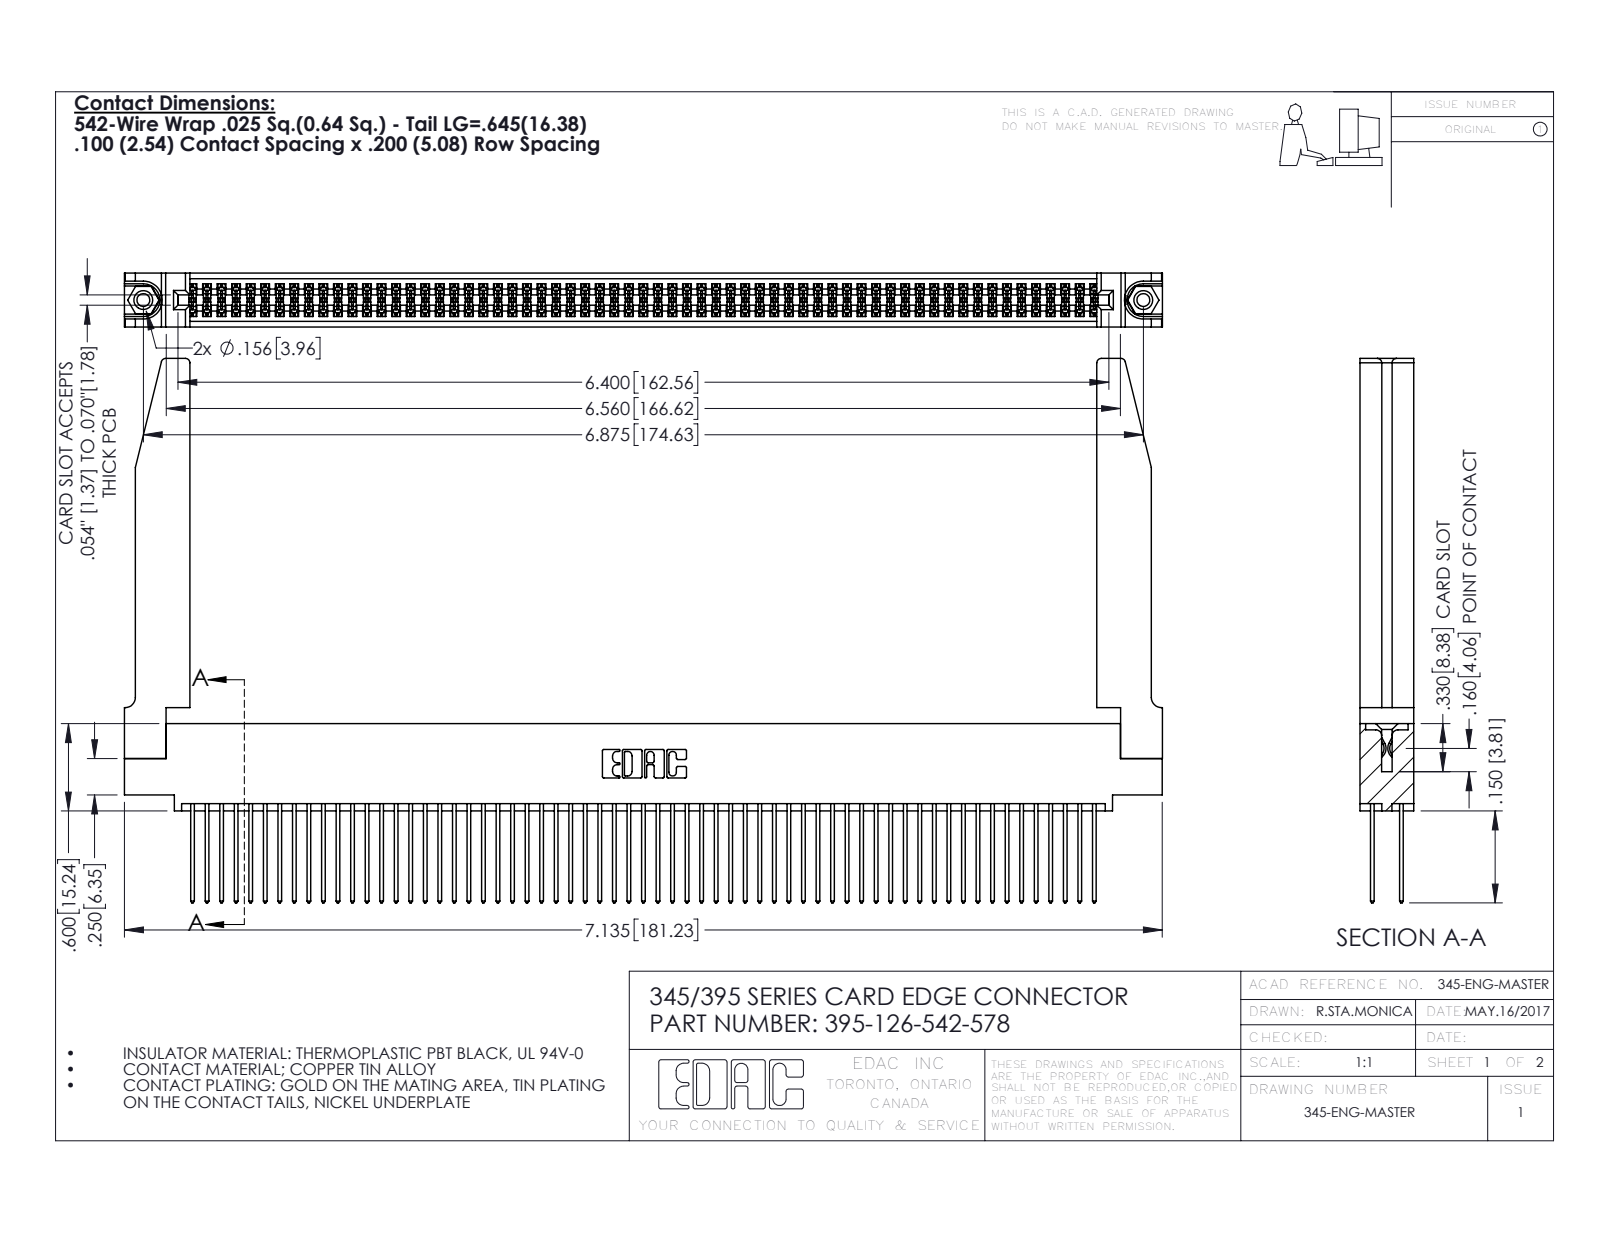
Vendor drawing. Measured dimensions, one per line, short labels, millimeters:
name: 345-292-001_345-293-142; 345-250-001_345-250-001-102; 345-220-078_345-220-078; 345 Part_0.110 Offset - 0.156 Dia-TH (+1 more)
written by: SolidWorks 2016 (CONFIG_CONTROL_DESIGN)
unit: mm
bodies: 131 solids, 6664 faces (4384 planar, 2228 cylindrical, 52 other)
size: 181.3 × 95 × 9.4
volume: 26 090 mm³; area: 37 150 mm²
holes: 2× ⌀2.3, 2× ⌀3.2, 2× ⌀4, 1× ⌀1.6
bosses: 2× ⌀3.9
rounds: 189× R0.2, 126× R0.3, 22× R0.3, 8× R0.8, 6× R0.2, 6× R0.8, 3× R0.7, 2× R0.4
face distances: 1.8, 7.6, 9.4, 5.1, 2.5, 6.9, 0.6, 5.7, 4.4, 3.8
hole spacings: 6.9, 168.6, 174.6
